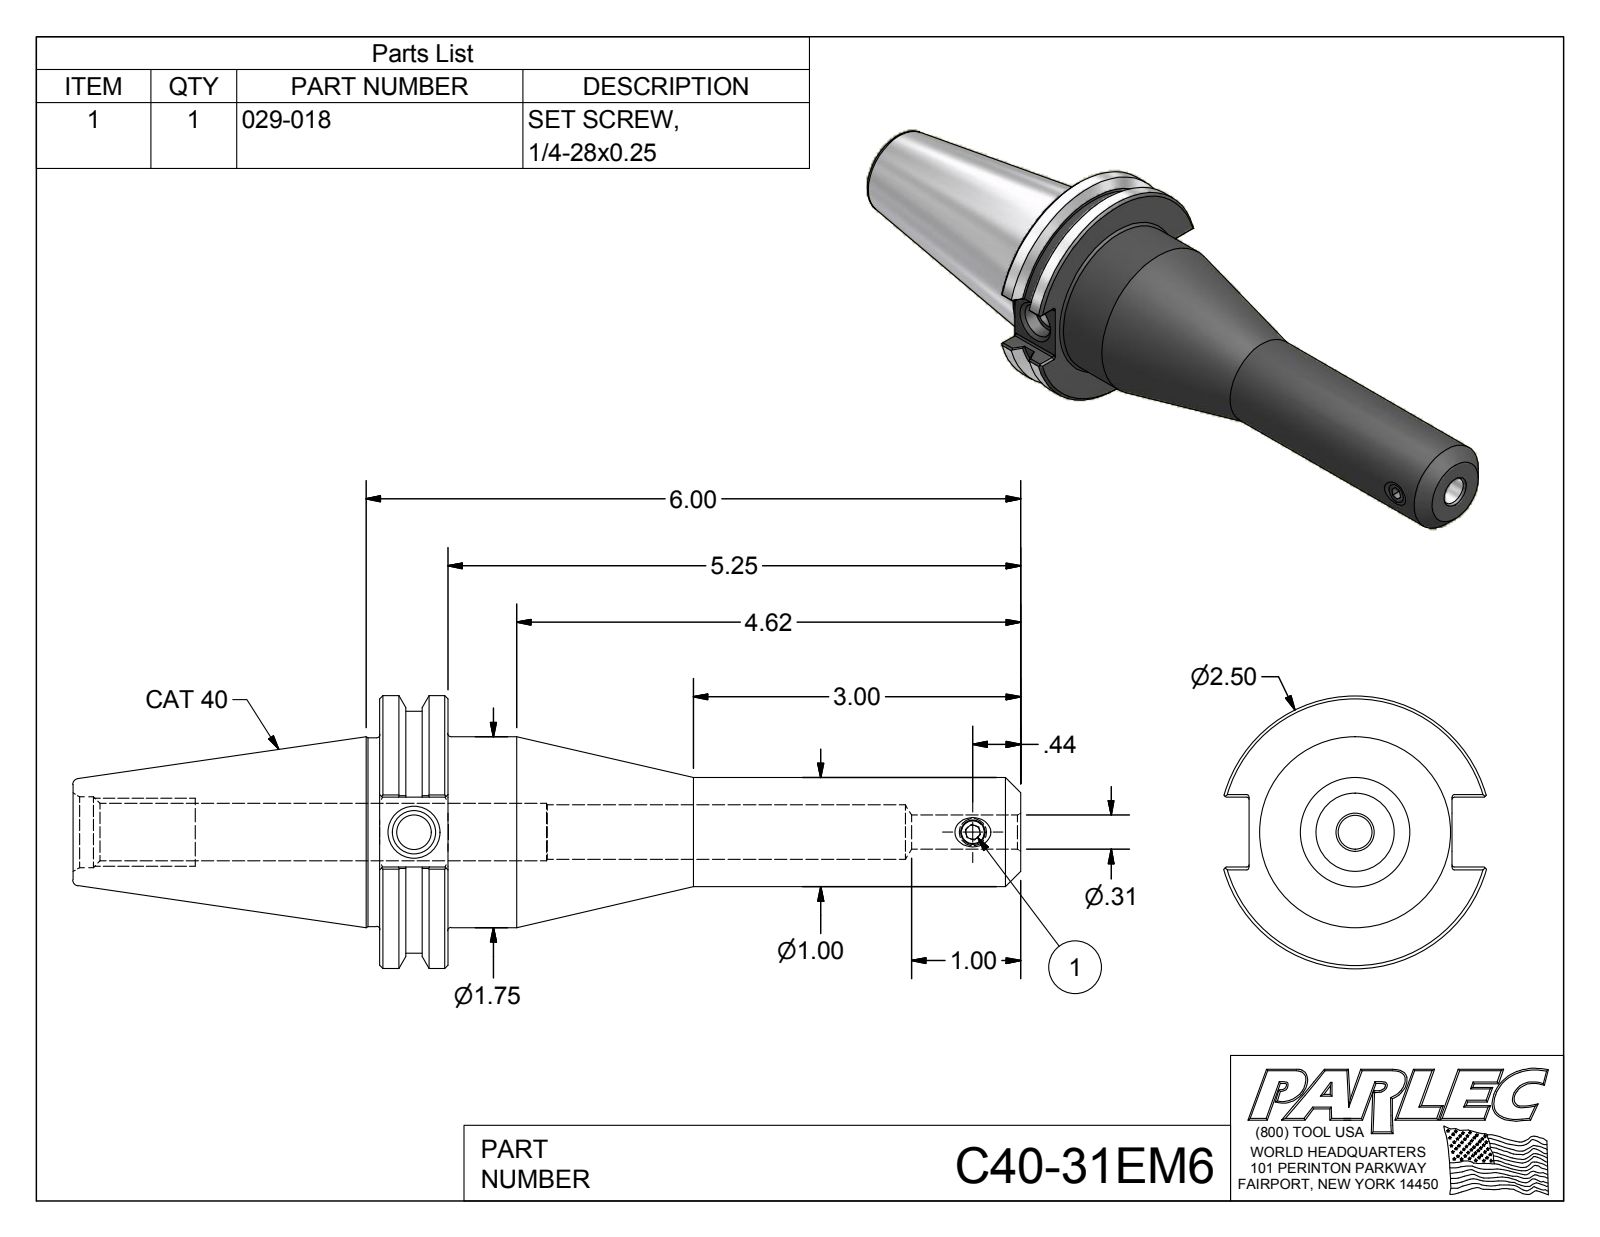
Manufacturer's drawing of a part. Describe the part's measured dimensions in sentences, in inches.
The part is named "C40-31EM6; C40-31EM6-1; 029-018". Its 3-D file was written by "Autodesk Inventor 2012 (AUTOMOTIVE_DESIGN)". It is 2 solids with 102 faces: 40 planar, 29 cylindrical and 33 other. Overall it measures 8.687 by 2.5 by 2.406 inches. Its volume is 11.5 cubic inches and its surface area 57.77 square inches. Round holes: 1 of diameter 0.211, 1 of diameter 0.313, 1 of diameter 0.315, 1 of diameter 0.399, 1 of diameter 0.5, 1 of diameter 0.527, 1 of diameter 0.648. Round bosses or shafts: 1 of diameter 2.5, 1 of diameter 2.219, 1 of diameter 1.75, 1 of diameter 1.73, 1 of diameter 1, 1 of diameter 0.25. Partial cylindrical surfaces (rounded edges, fillets, slot ends): 12 of radius 0.02. The main face-to-face distances are 0.625, 5.875, 5.25, 0.64, 1.86, 2.812, 3.437, 8.687, 3.201, 0.389. The hole center spacings are 5.122.
